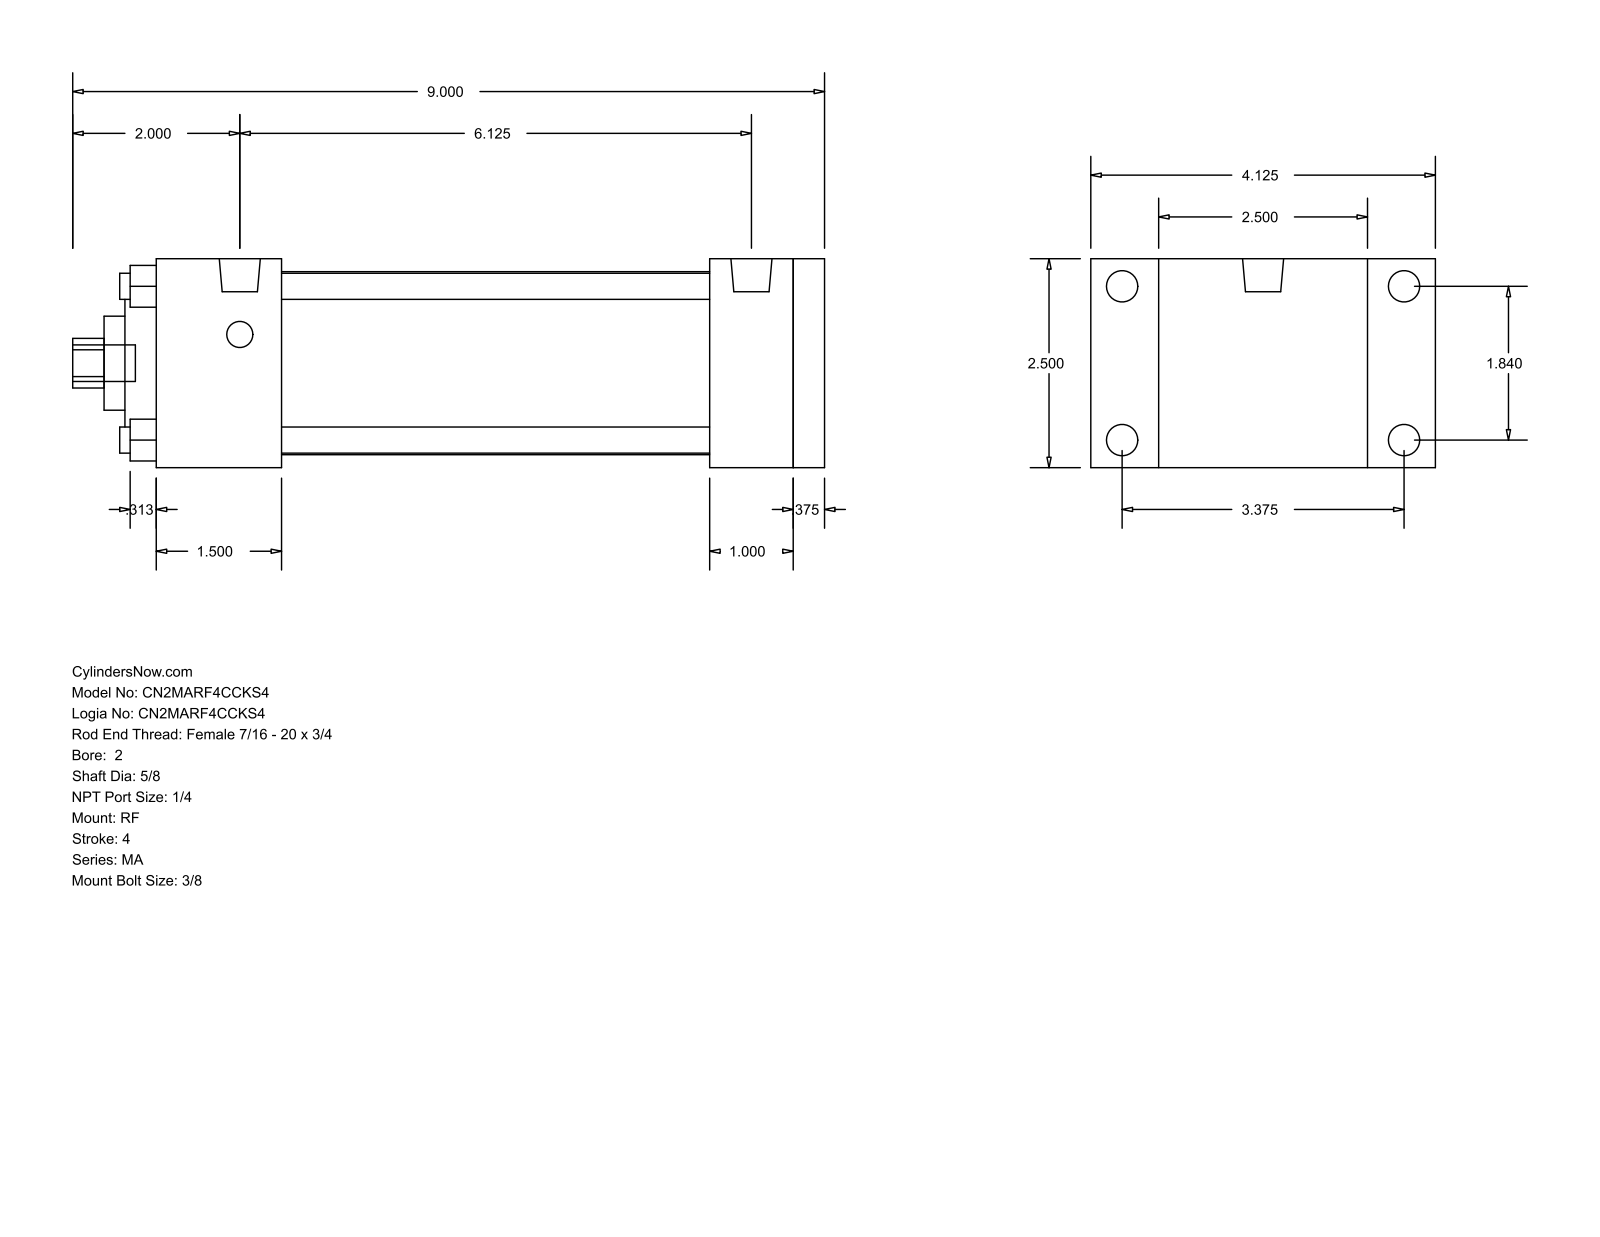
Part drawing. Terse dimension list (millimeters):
name: MA_RF__0200_0.625
written by: GSSL Pune (CONFIG_CONTROL_DESIGN)
unit: mm
bodies: 0 solids, 94 faces (65 planar, 29 cylindrical, 0 other)
size: 228.6 × 104.78 × 63.5
holes: 4× ⌀7.94, 1× ⌀15.88, 1× ⌀28.57, 1× ⌀50.8, 1× ⌀55.63
bosses: 4× ⌀9.53, 4× ⌀7.94, 2× ⌀12.49, 1× ⌀11.11
rounds: 1× R7.54
face distances: 63.5, 9.53, 38.1, 9.52, 193.67, 203.2, 212.72, 155.57, 165.1, 168.28
hole spacings: 33.05, 46.74, 66.1
